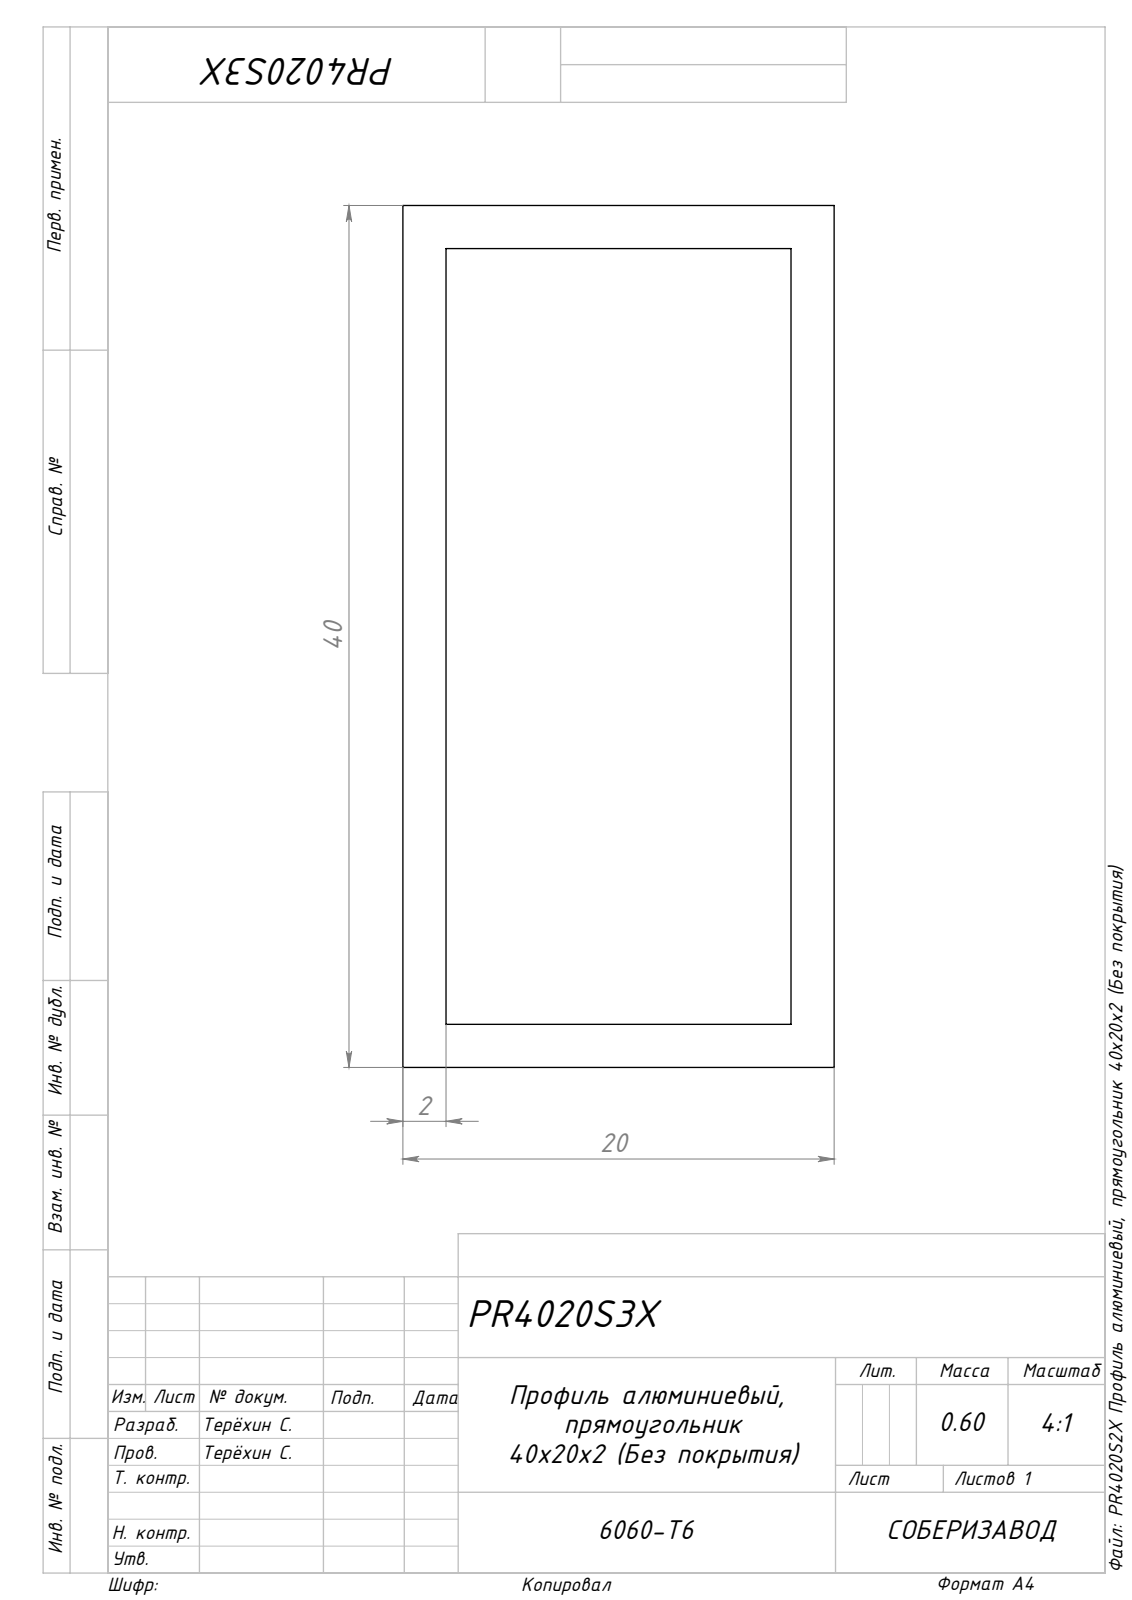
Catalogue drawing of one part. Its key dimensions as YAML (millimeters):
part_name: "PR4020S3X Профиль алюминиевый, прямоугольник 40x20x2 (Без покрытия)"
step_written_by: "SolidWorks 2025 (AUTOMOTIVE_DESIGN)"
units: millimeters
bodies: {solids: 1, faces: 10, planar: 10, cylindrical: 0, other: 0}
overall_size: [1000, 40, 20]
volume: 224000
surface_area: 224448
face_to_face_distances: [2, 18, 20, 16, 38, 40, 36, 1000]
